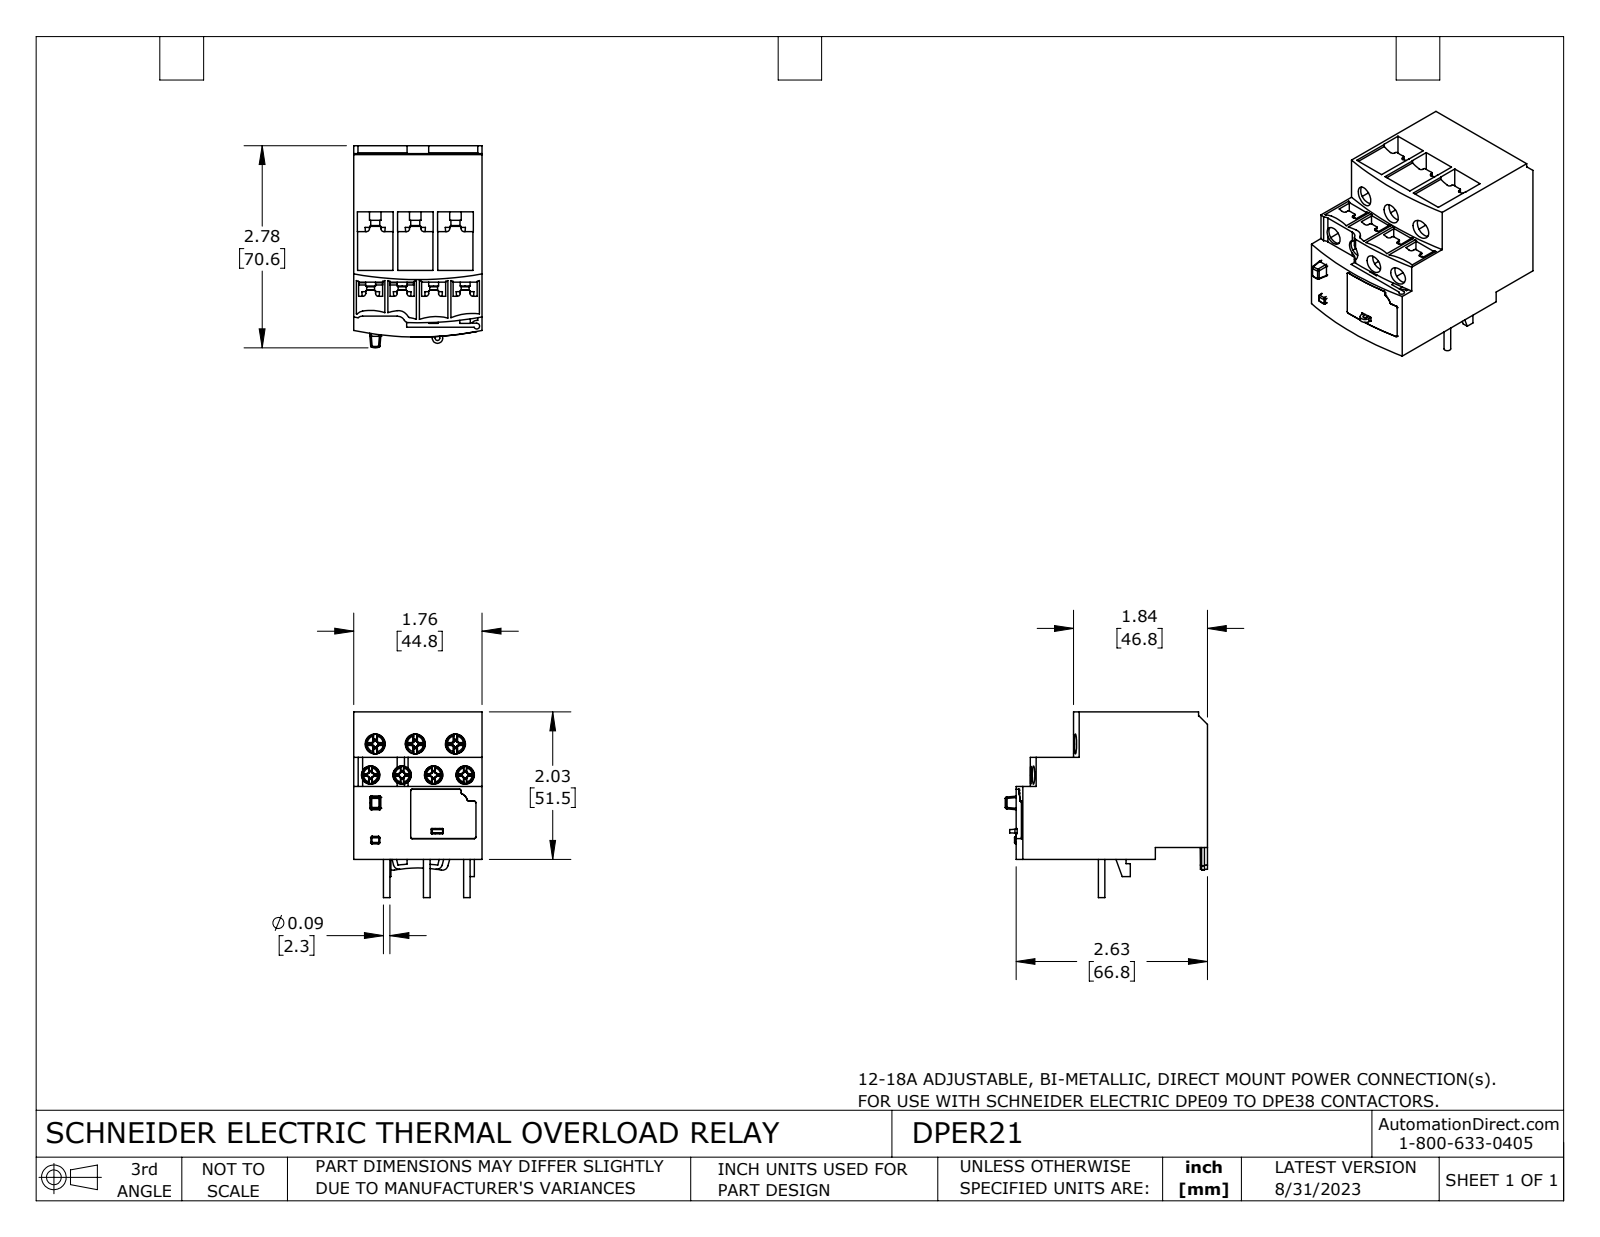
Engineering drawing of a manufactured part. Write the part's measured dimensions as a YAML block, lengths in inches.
part_name: "DPER21"
step_written_by: "SolidWorks 2021 (CONFIG_CONTROL_DESIGN)"
units: inches
bodies: {solids: 16, faces: 1212, planar: 676, cylindrical: 269, other: 267}
overall_size: [2.778, 2.553, 1.764]
volume: 6.953
surface_area: 47.15
round_holes:
  - {diameter: 0.252, count: 4}
  - {diameter: 0.276, count: 3}
  - {diameter: 0.079, count: 2}
  - {diameter: 0.118, count: 2}
  - {diameter: 0.059, count: 1}
  - {diameter: 0.244, count: 1}
round_bosses_or_shafts:
  - {diameter: 0.091, count: 12}
  - {diameter: 0.138, count: 4}
  - {diameter: 0.108, count: 4}
  - {diameter: 0.157, count: 3}
  - {diameter: 0.154, count: 3}
  - {diameter: 0.124, count: 3}
  - {diameter: 0.118, count: 1}
  - {diameter: 0.107, count: 1}
partial_cylinders:
  - {radius: 0.02, count: 52}
  - {radius: 0.039, count: 22}
  - {radius: 0.004, count: 19}
  - {radius: 0.012, count: 8}
  - {radius: 0.008, count: 6}
  - {radius: 0.63, count: 6}
  - {radius: 0.079, count: 4}
  - {radius: 0.024, count: 2}
face_to_face_distances: [1.764, 0.165, 2.028, 1.863, 0.909, 0.551, 0.618, 1.409, 1.245, 2.497]
hole_center_spacings: [0.433, 0.551, 0.866, 0.334, 0.381, 0.404, 0.422, 0.449]
